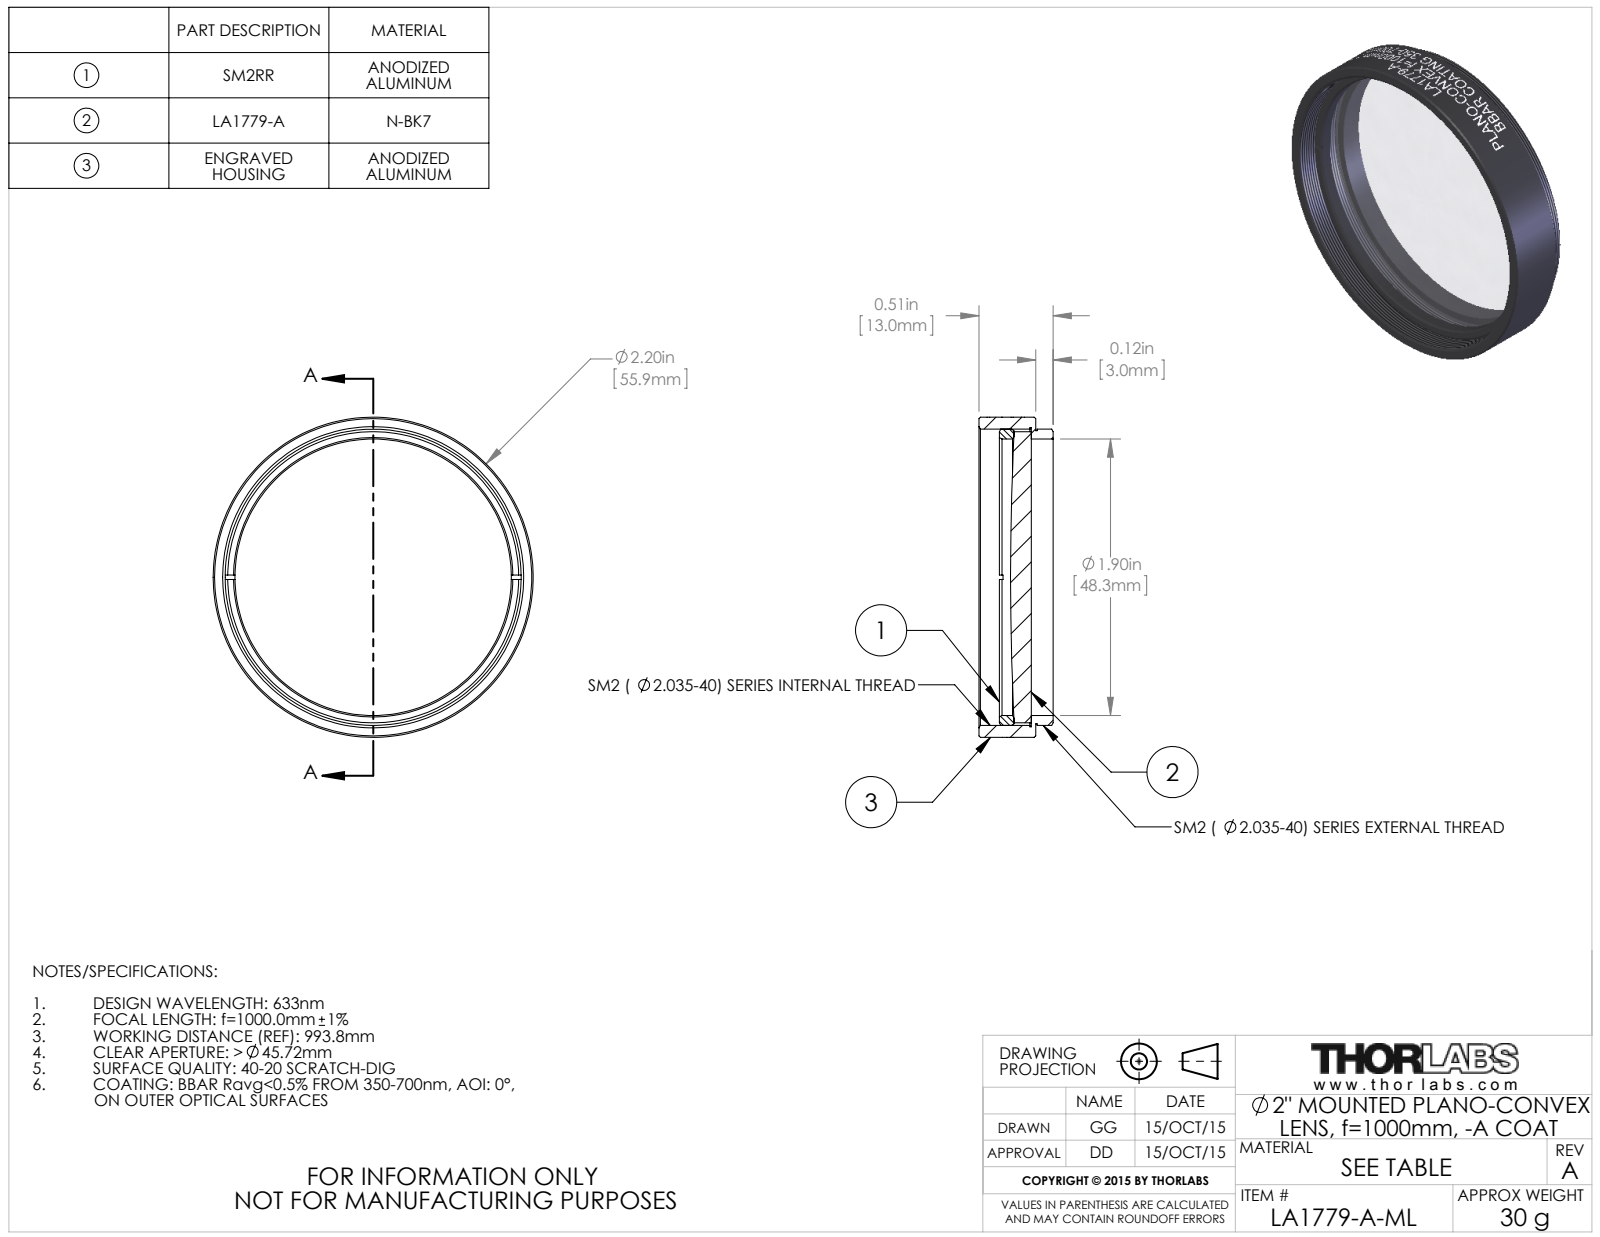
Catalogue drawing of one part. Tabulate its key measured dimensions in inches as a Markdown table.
| quantity | value |
| --- | --- |
| part name | TTN039633-E0W |
| STEP written by | SolidWorks 2014 (CONFIG_CONTROL_DESIGN) |
| units | inches |
| bodies | 3 solids, 141 faces (16 planar, 105 cylindrical, 20 other) |
| overall size | 2.2 × 2.2 × 0.51 |
| volume | 0.722 in³ |
| surface area | 17.59 in² |
| round holes (diameter × count) | 1.9 × 1, 2.055 × 1 |
| round bosses / shafts (diameter × count) | 2.2 × 1, 2.035 × 1, 2.015 × 1, 2 × 1 |
| main face-to-face distances | 0.03, 0.39, 0.36, 0.12, 0.15, 0.51, 0.27, 0.15, 0.12, 0.241 |
